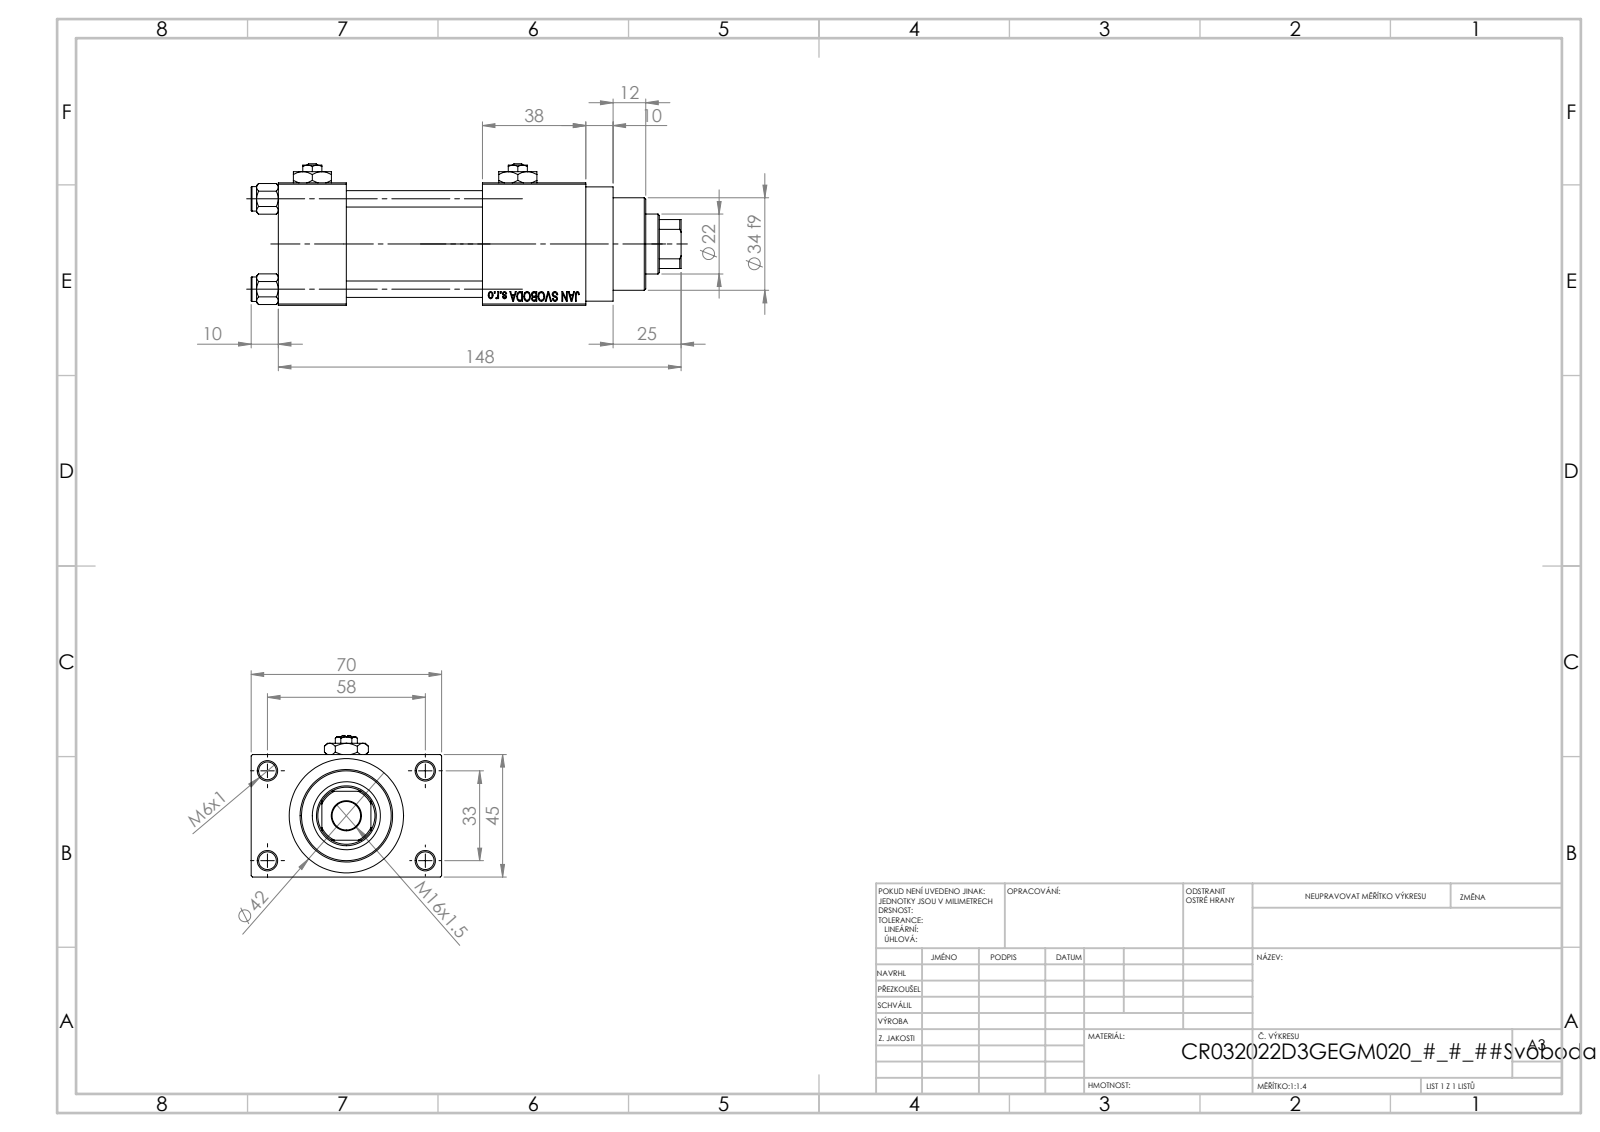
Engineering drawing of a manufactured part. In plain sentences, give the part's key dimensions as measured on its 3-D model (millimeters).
The part is named "V215CR_D_Body; V215CR_VCP_D; NUT_M5_D; Zatka_pro_OIL_PORT (+2 more)". Its 3-D file was written by "SolidWorks 2019 (CONFIG_CONTROL_DESIGN)". It is 13 solids with 1202 faces: 542 planar, 100 cylindrical and 560 other. Overall it measures 158 by 70 by 52 millimeters. Its volume is 243 368 cubic millimeters and its surface area 81 200 square millimeters. Round holes: 4 of diameter 6, 4 of diameter 6.5, 2 of diameter 7, 2 of diameter 13.16, 2 of diameter 20, 1 of diameter 10.5, 1 of diameter 22, 1 of diameter 24, 1 of diameter 25, 1 of diameter 32, 1 of diameter 33. Round bosses or shafts: 4 of diameter 9, 1 of diameter 42, 1 of diameter 38, 1 of diameter 34. Partial cylindrical surfaces (rounded edges, fillets, slot ends): 1 of radius 10.5. The main face-to-face distances are 45, 25, 12.5, 57.5, 50, 75, 88, 70, 38, 113. The hole center spacings are 12.4, 23.48, 33.2, 33.37, 35.35, 45.6, 56.35, 33.
